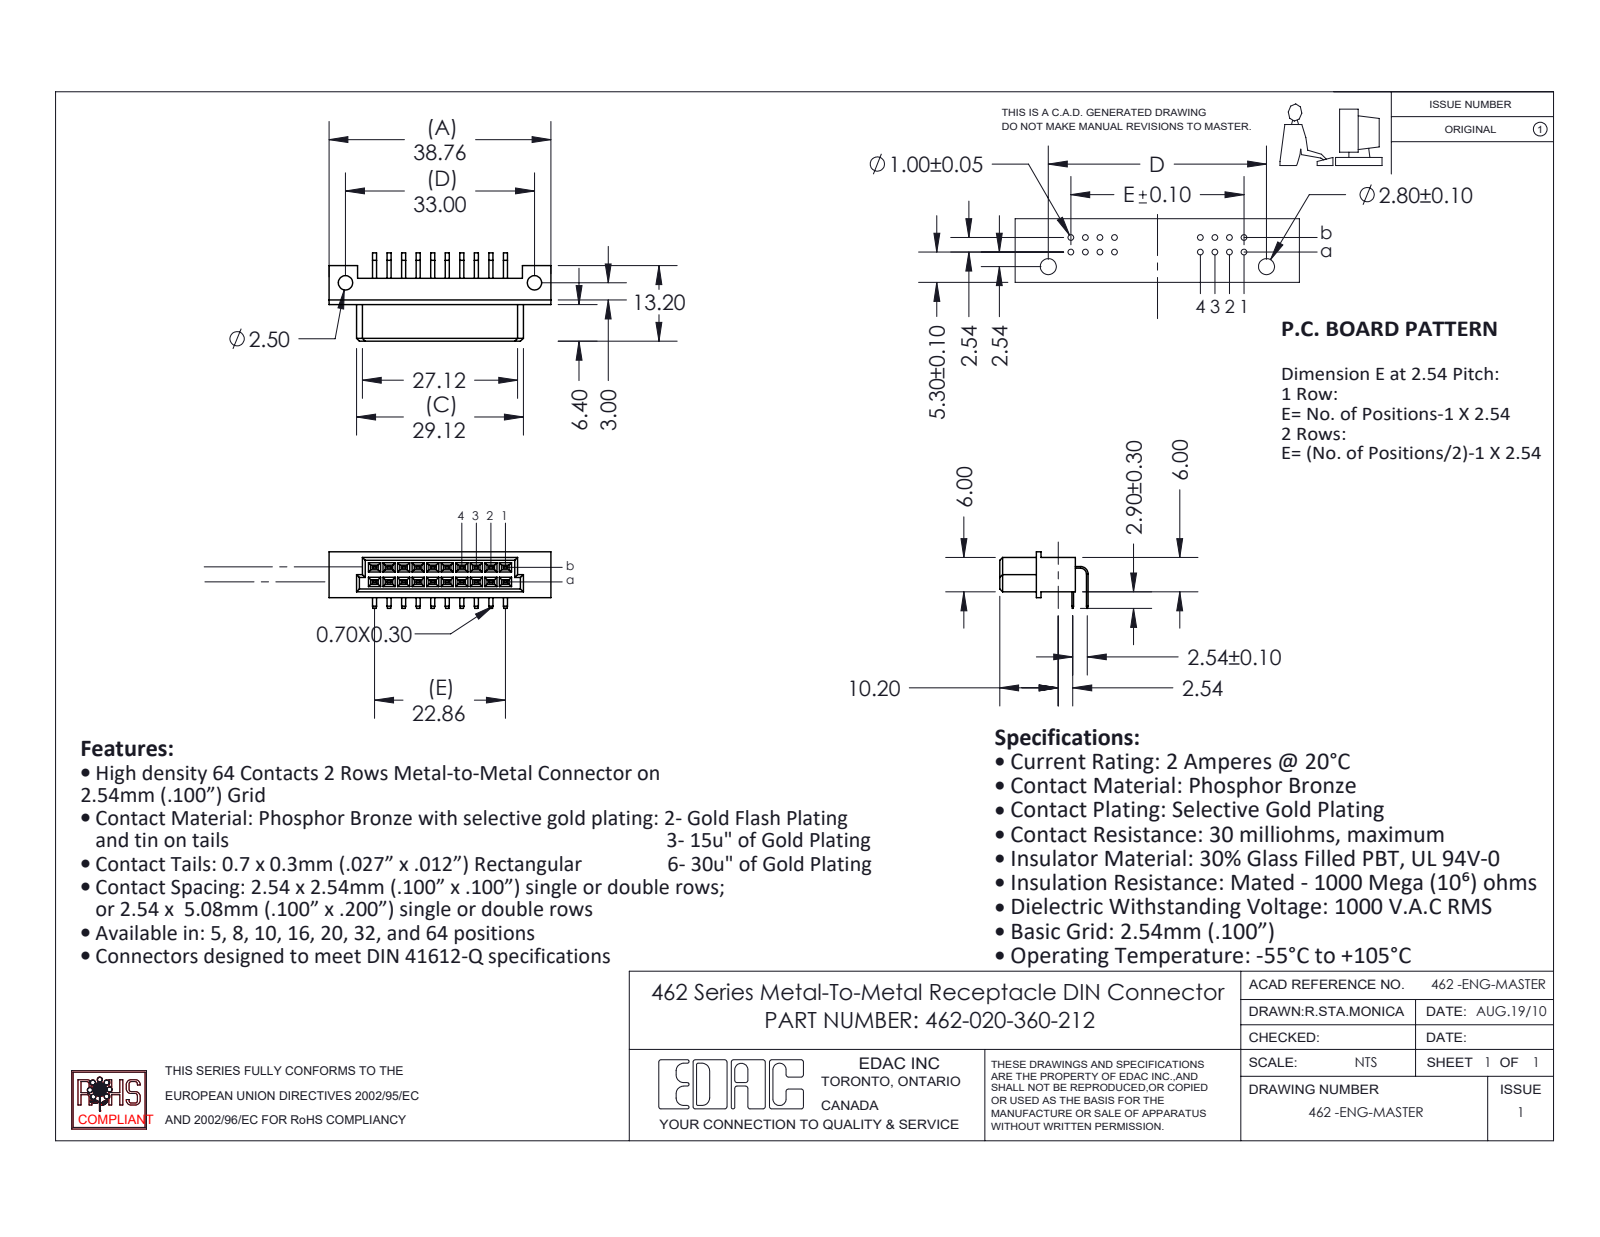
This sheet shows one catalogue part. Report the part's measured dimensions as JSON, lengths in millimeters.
{"part_name": "462-020-360-212; 462-290-2; 462 Part_20; 462-290-1", "step_written_by": "SolidWorks 2020 (CONFIG_CONTROL_DESIGN)", "units": "millimeters", "bodies": {"solids": 21, "faces": 575, "planar": 531, "cylindrical": 44, "other": 0}, "overall_size": [38.76, 15.43, 9.9], "volume_mm3": 2160, "surface_area_mm2": 2803, "round_holes": [[2.5, 2]], "partial_cylinders_radius": [[1.02, 2], [1.32, 2]], "face_to_face_distances": [2.54, 6, 4.6, 0.81, 1.58, 1.88, 4.12, 4.42, 0.56, 0.55], "hole_center_spacings": [33]}
